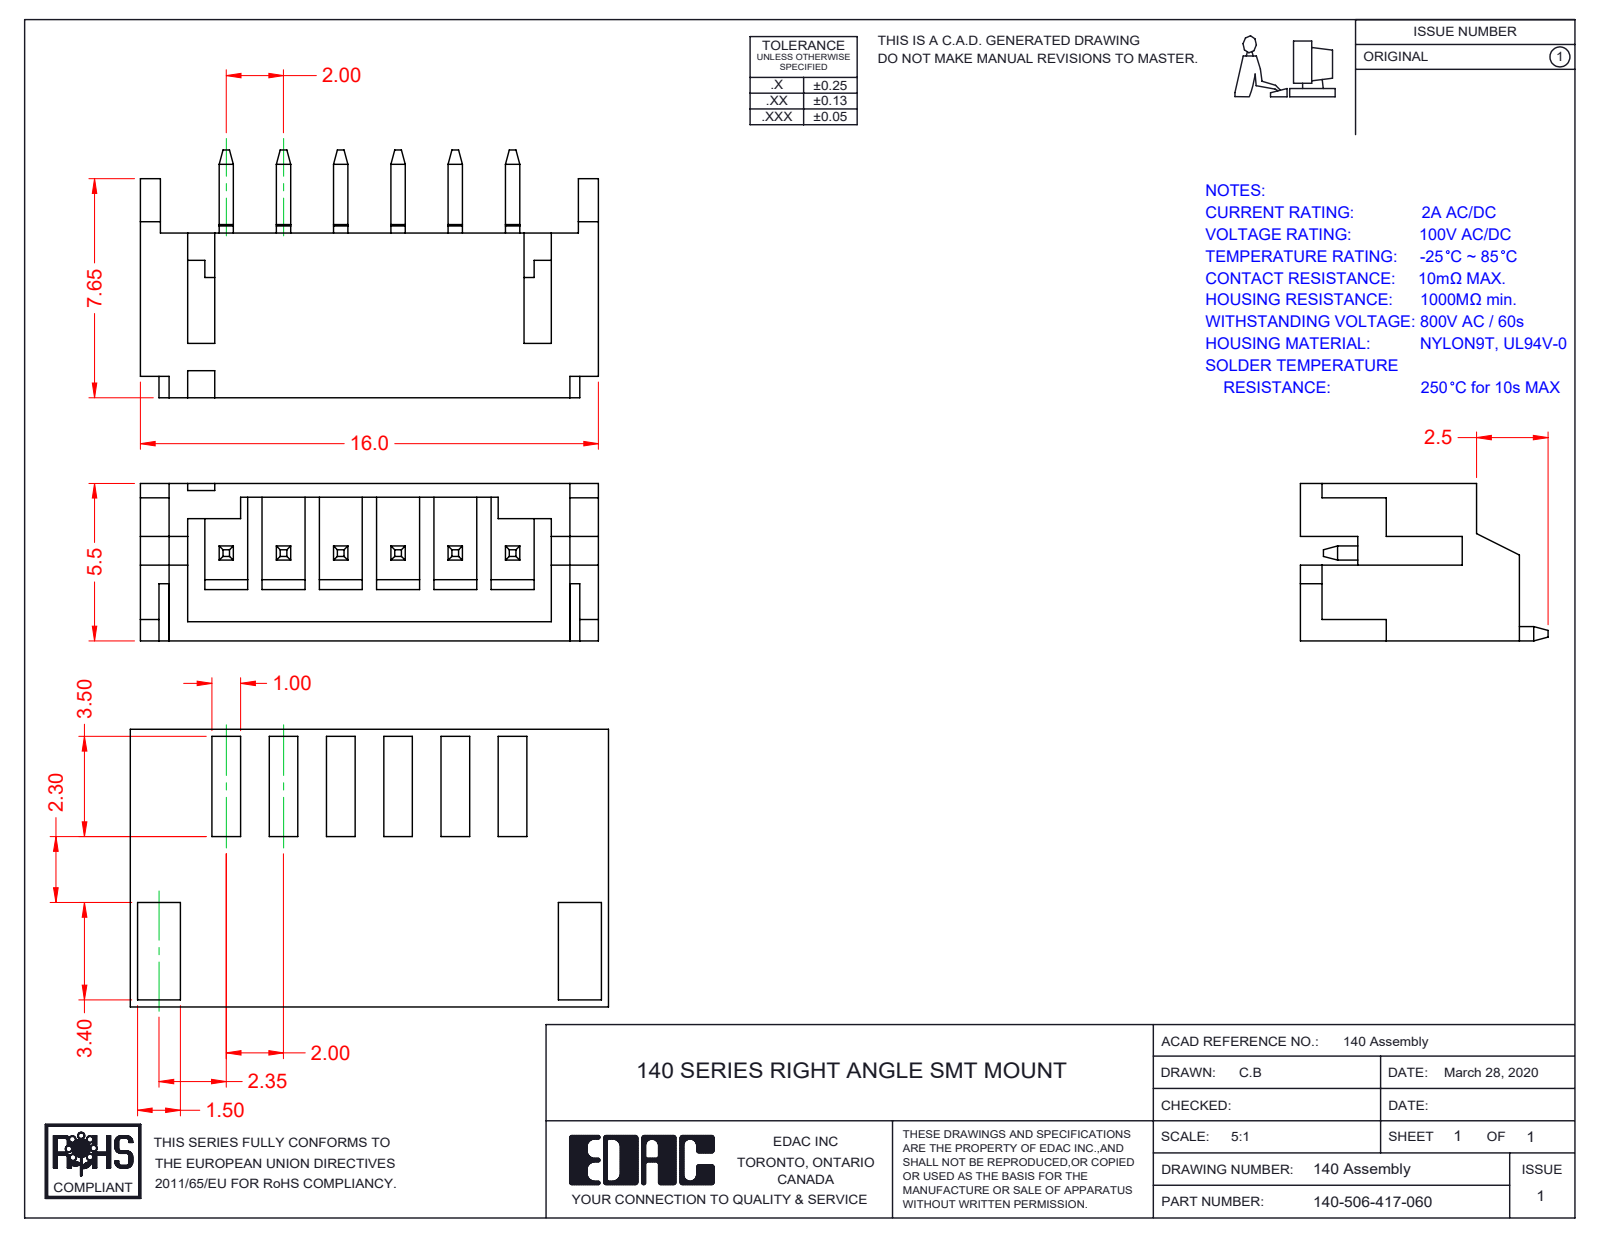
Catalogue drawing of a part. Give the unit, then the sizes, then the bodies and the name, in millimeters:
Units: millimetres
Overall size (bounding box): 16 × 8.65 × 5.5
Partial cylindrical surfaces — rounded edges, fillets, slot ends (radius × count): R0.55 ×2
Main face-to-face distances: 0.65, 5.5, 0.67, 1, 0.5, 4.83, 14.35, 0.95, 1.65, 2
Volume: 235 mm³ · Surface area: 862 mm²
Bodies: 9 solids, 356 faces (332 planar, 24 cylindrical, 0 other)
Part name (STEP PRODUCT): RA SMT Contact; RA SMT Pad; 140-506-417-060; RA SMT Housing_506
STEP written by: SolidWorks 2016 (CONFIG_CONTROL_DESIGN)
